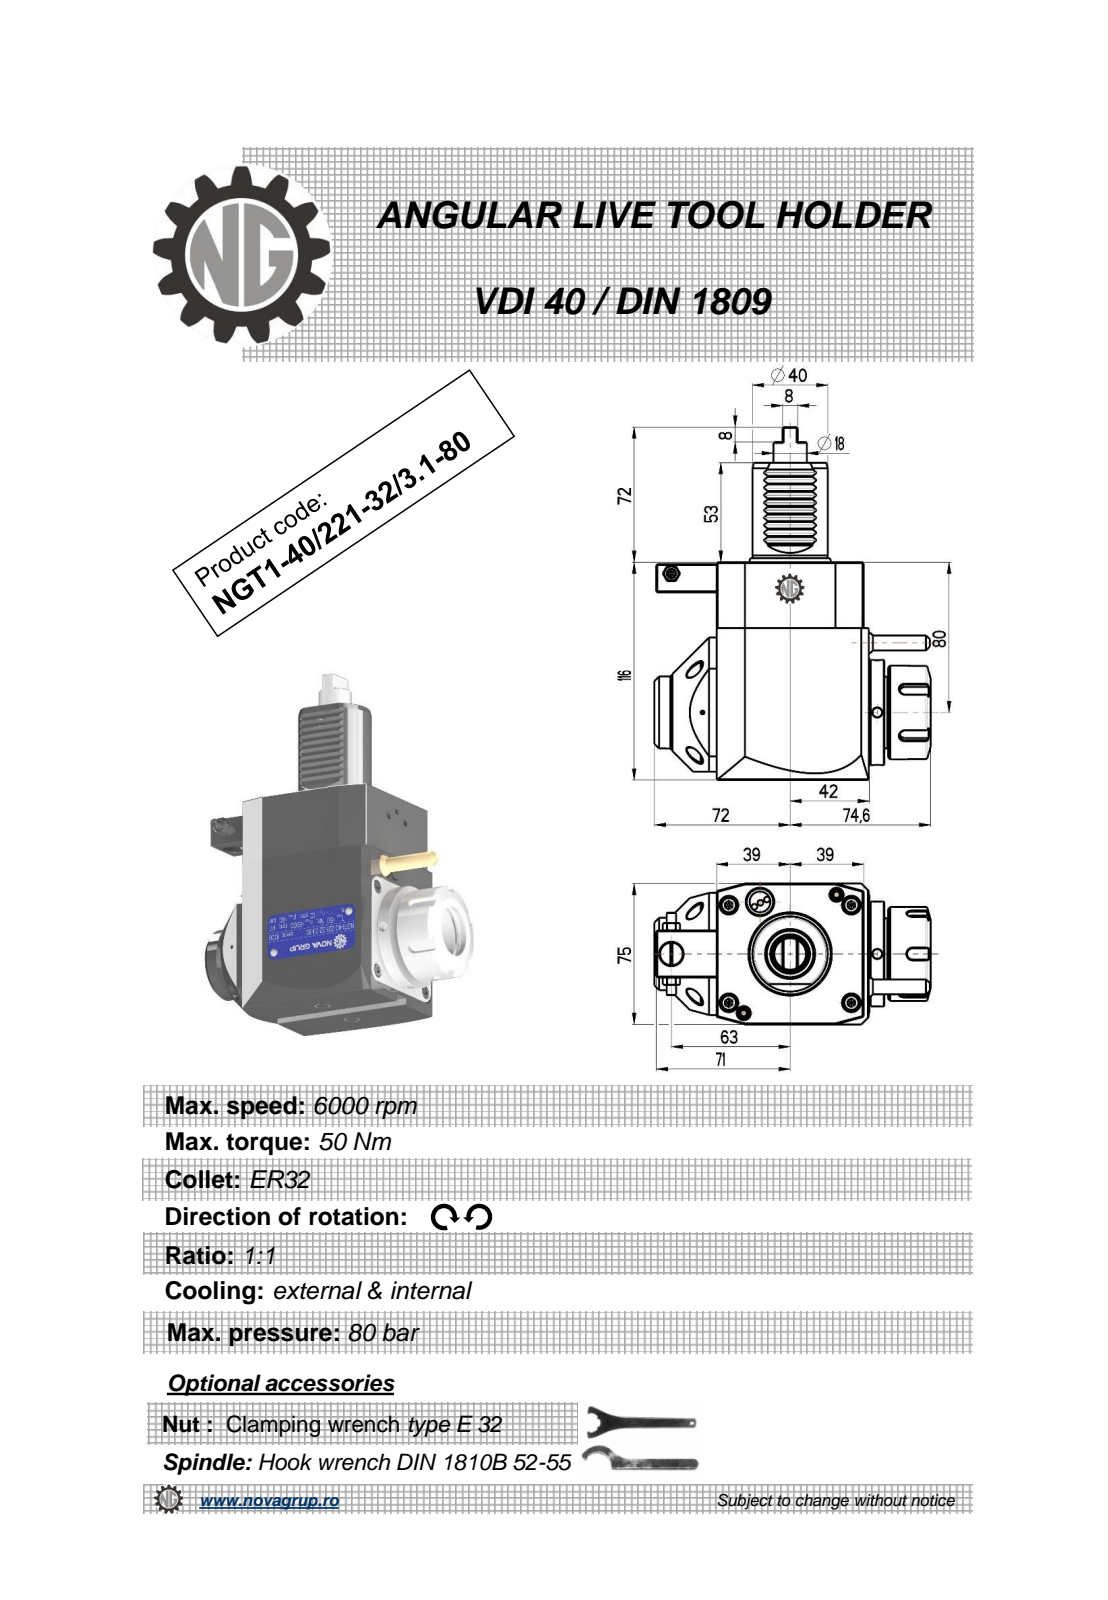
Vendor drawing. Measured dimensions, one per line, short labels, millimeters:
name: NGT1_40_221_32_3_1_80
written by: PRO/ENGINEER BY PARAMETRIC TECHNOLOGY CORPORATION, 2010280 (CONFIG_CONTROL_DESIGN)
unit: mm
bodies: 1 solid, 415 faces (193 planar, 87 cylindrical, 135 other)
size: 188 × 146.6 × 75
volume: 903 027 mm³; area: 72 453 mm²
holes: 3× ⌀5, 1× ⌀3, 1× ⌀4.2, 1× ⌀9.5, 1× ⌀12, 1× ⌀27
bosses: 1× ⌀56, 1× ⌀50, 1× ⌀43, 1× ⌀40, 1× ⌀38.5, 1× ⌀17.8, 1× ⌀11.2, 1× ⌀8.96
rounds: 12× R0.26, 10× R0.3, 6× R0.22, 5× R3, 2× R0.8, 1× R0.5, 1× R40
face distances: 75, 116, 81, 78, 3, 111, 80.8, 2.8, 7.5, 0.5
hole spacings: 39.58, 40.93, 72.5, 109.25, 131.95
